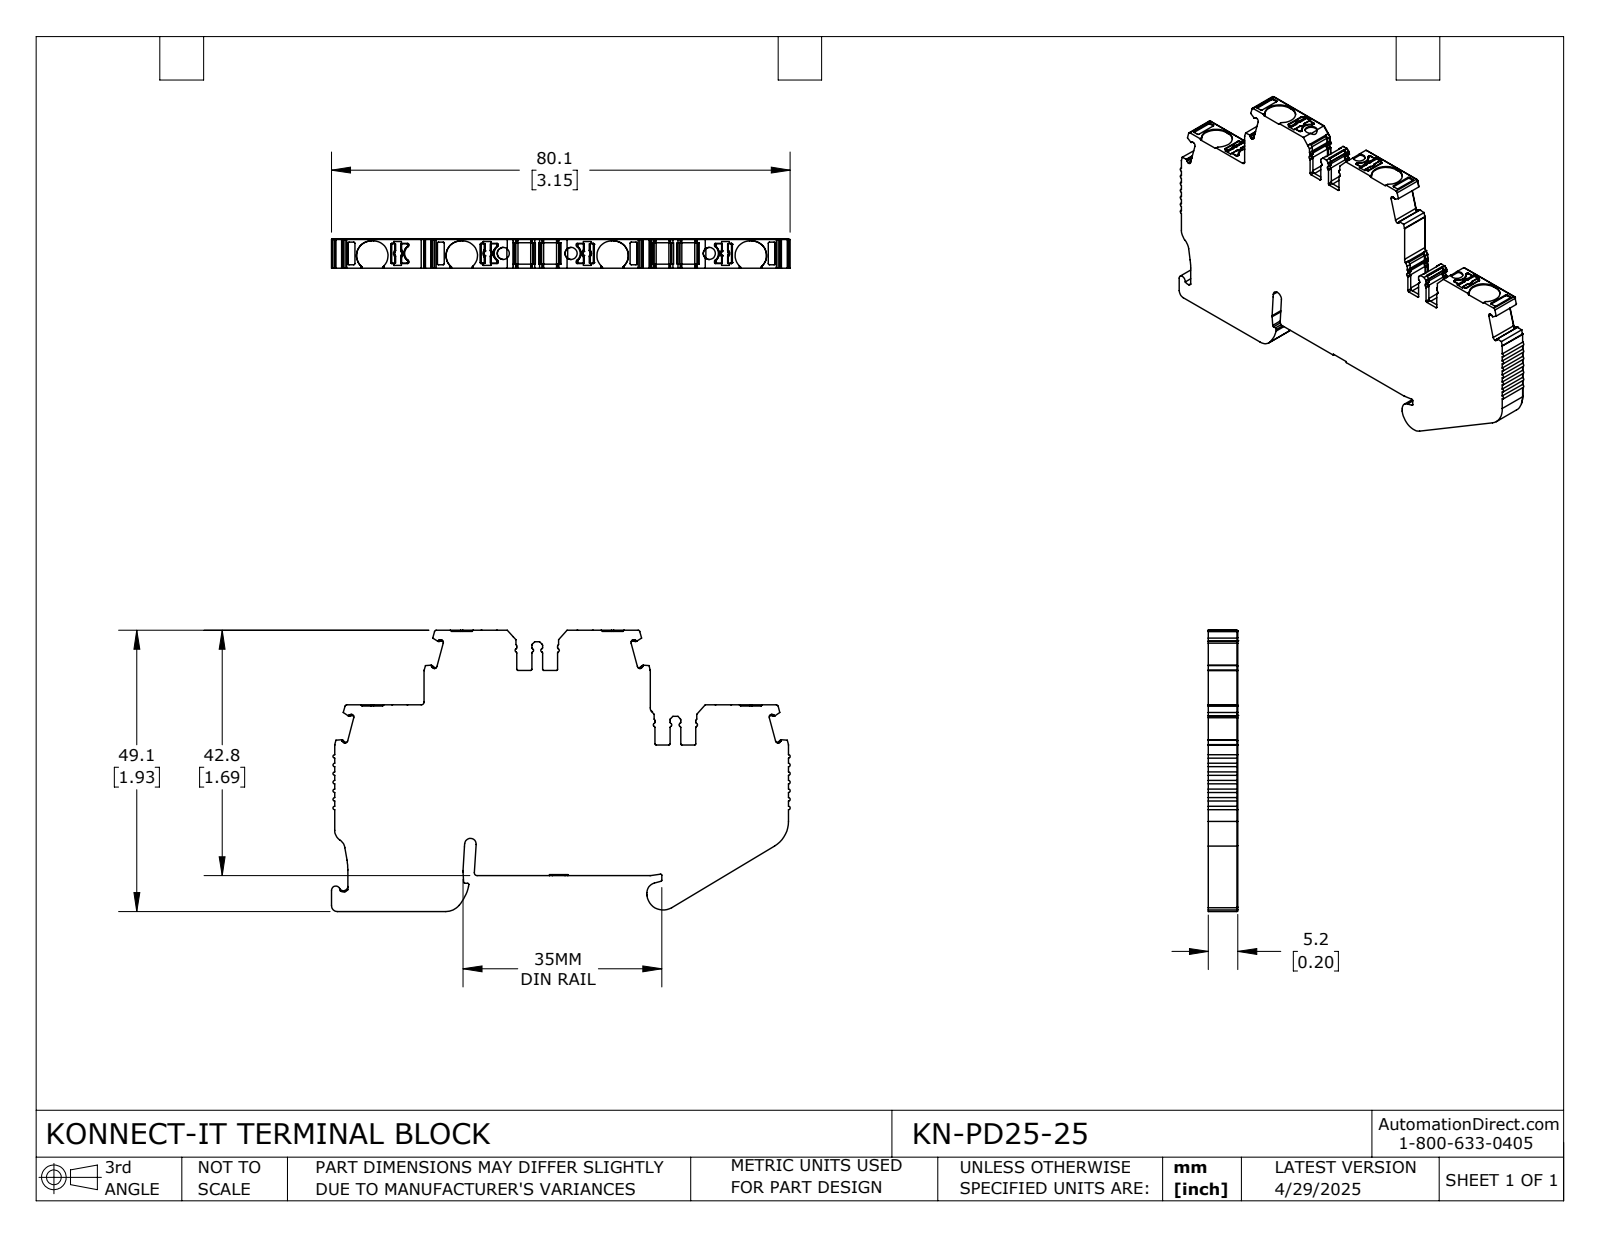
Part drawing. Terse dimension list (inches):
name: KN-PD25-25
written by: SolidWorks 2024 (CONFIG_CONTROL_DESIGN)
unit: in
bodies: 1 solid, 979 faces (470 planar, 438 cylindrical, 71 other)
size: 3.153 × 1.933 × 0.203
volume: 0.889 in³; area: 11.63 in²
holes: 3× ⌀0.083
rounds: 100× R0.008, 57× R0.012, 41× R0.004, 21× R0.02, 17× R0.016, 16× R0.006, 9× R0.024, 8× R0.006
face distances: 0.203, 0.512, 0.246, 1.678, 1.166, 1.924, 0.079, 1.412, 0.504, 0.95
hole spacings: 0.466, 0.95, 1.417
